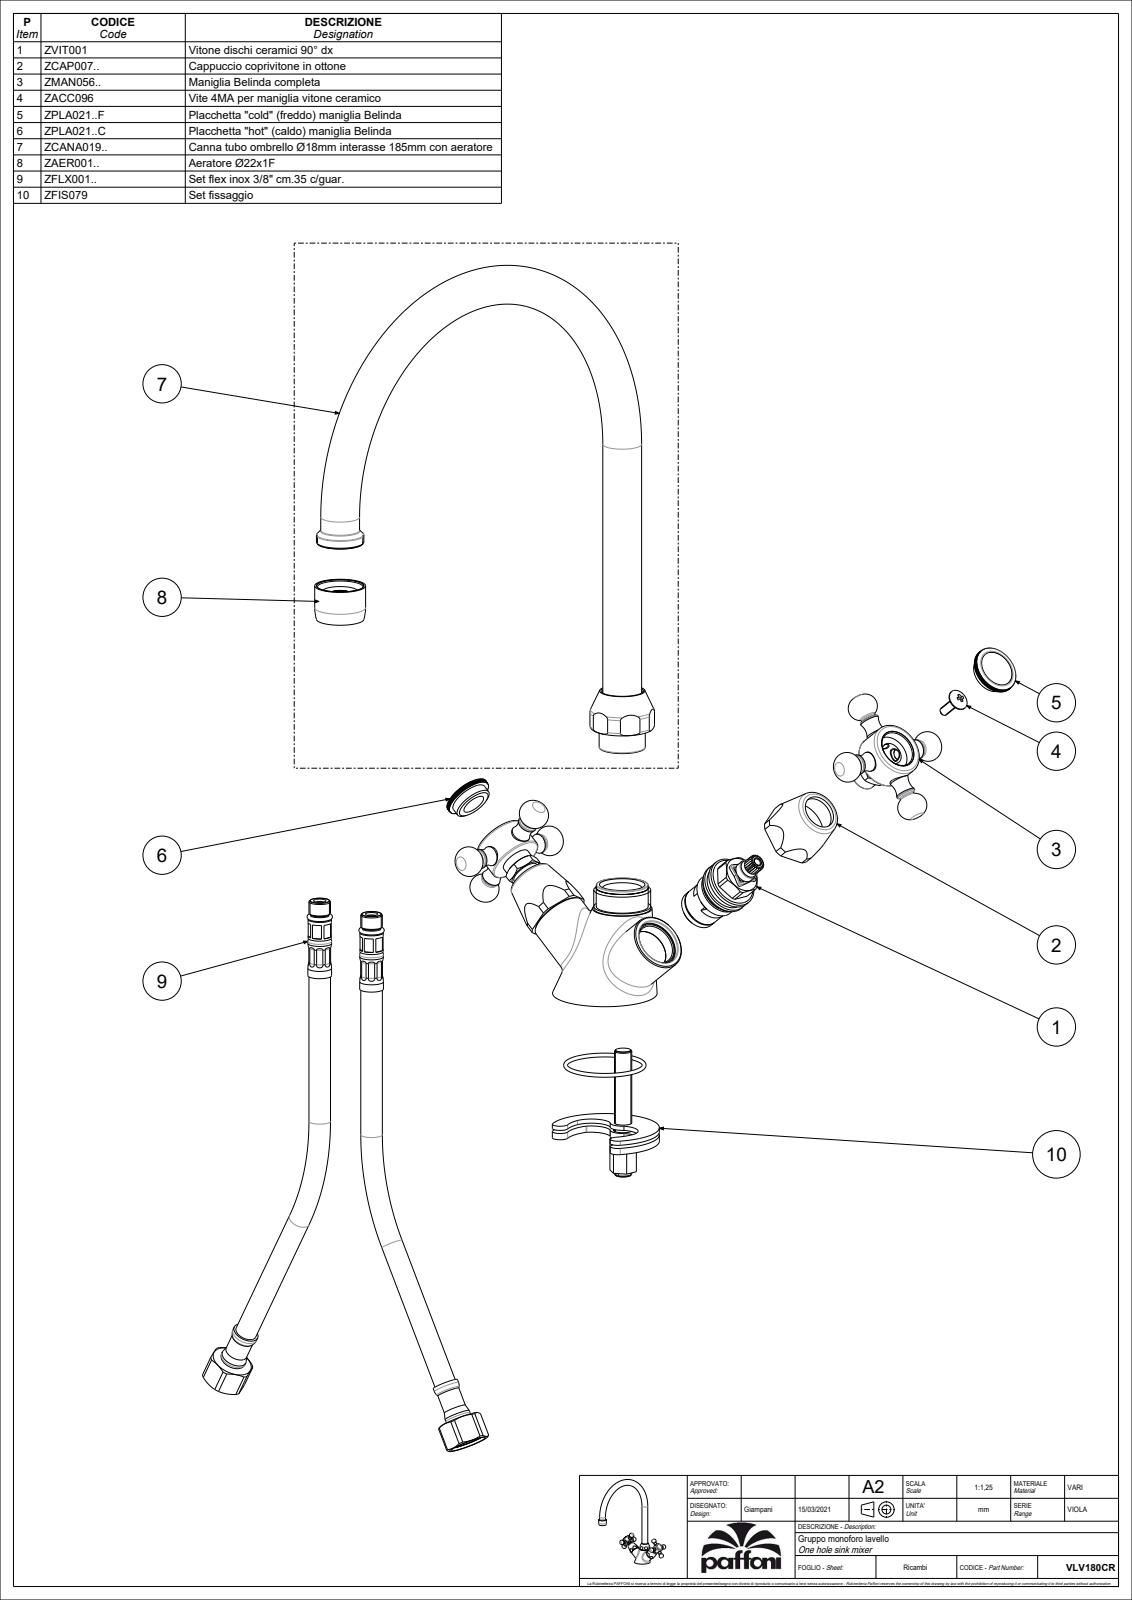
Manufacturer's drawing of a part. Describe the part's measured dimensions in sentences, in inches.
The part is named "VLV180CR". Its 3-D file was written by "CREO PARAMETRIC BY PTC INC, 2020044 (CONFIG_CONTROL_DESIGN)". It is 1 solid with 1222 faces: 564 planar, 394 cylindrical and 264 other. Overall it measures 10.949 by 8.649 by 6.912 inches. Its volume is 12.68 cubic inches and its surface area 99.08 square inches. Round holes: 4 of diameter 0.354, 2 of diameter 0.433, 2 of diameter 0.618, 2 of diameter 0.709, 2 of diameter 0.748, 2 of diameter 0.827, 2 of diameter 0.846, 2 of diameter 0.906, 1 of diameter 0.236, 1 of diameter 0.268, 1 of diameter 0.63, 1 of diameter 0.713. Round bosses or shafts: 6 of diameter 0.354, 6 of diameter 0.276, 2 of diameter 1.035, 2 of diameter 0.984, 2 of diameter 0.709, 2 of diameter 0.551, 2 of diameter 0.512, 1 of diameter 1.339. Partial cylindrical surfaces (rounded edges, fillets, slot ends): 2 of radius 0.138, 2 of radius 0.433, 2 of radius 0.571, 1 of radius 0.591. The main face-to-face distances are 1.386, 0.866, 2.252, 1.043, 0.945, 6, 1.811, 0.441, 0.315, 0.051. The hole center spacings are 0.276, 0.527, 0.547, 0.024, 0.449, 0.472, 0.551.
